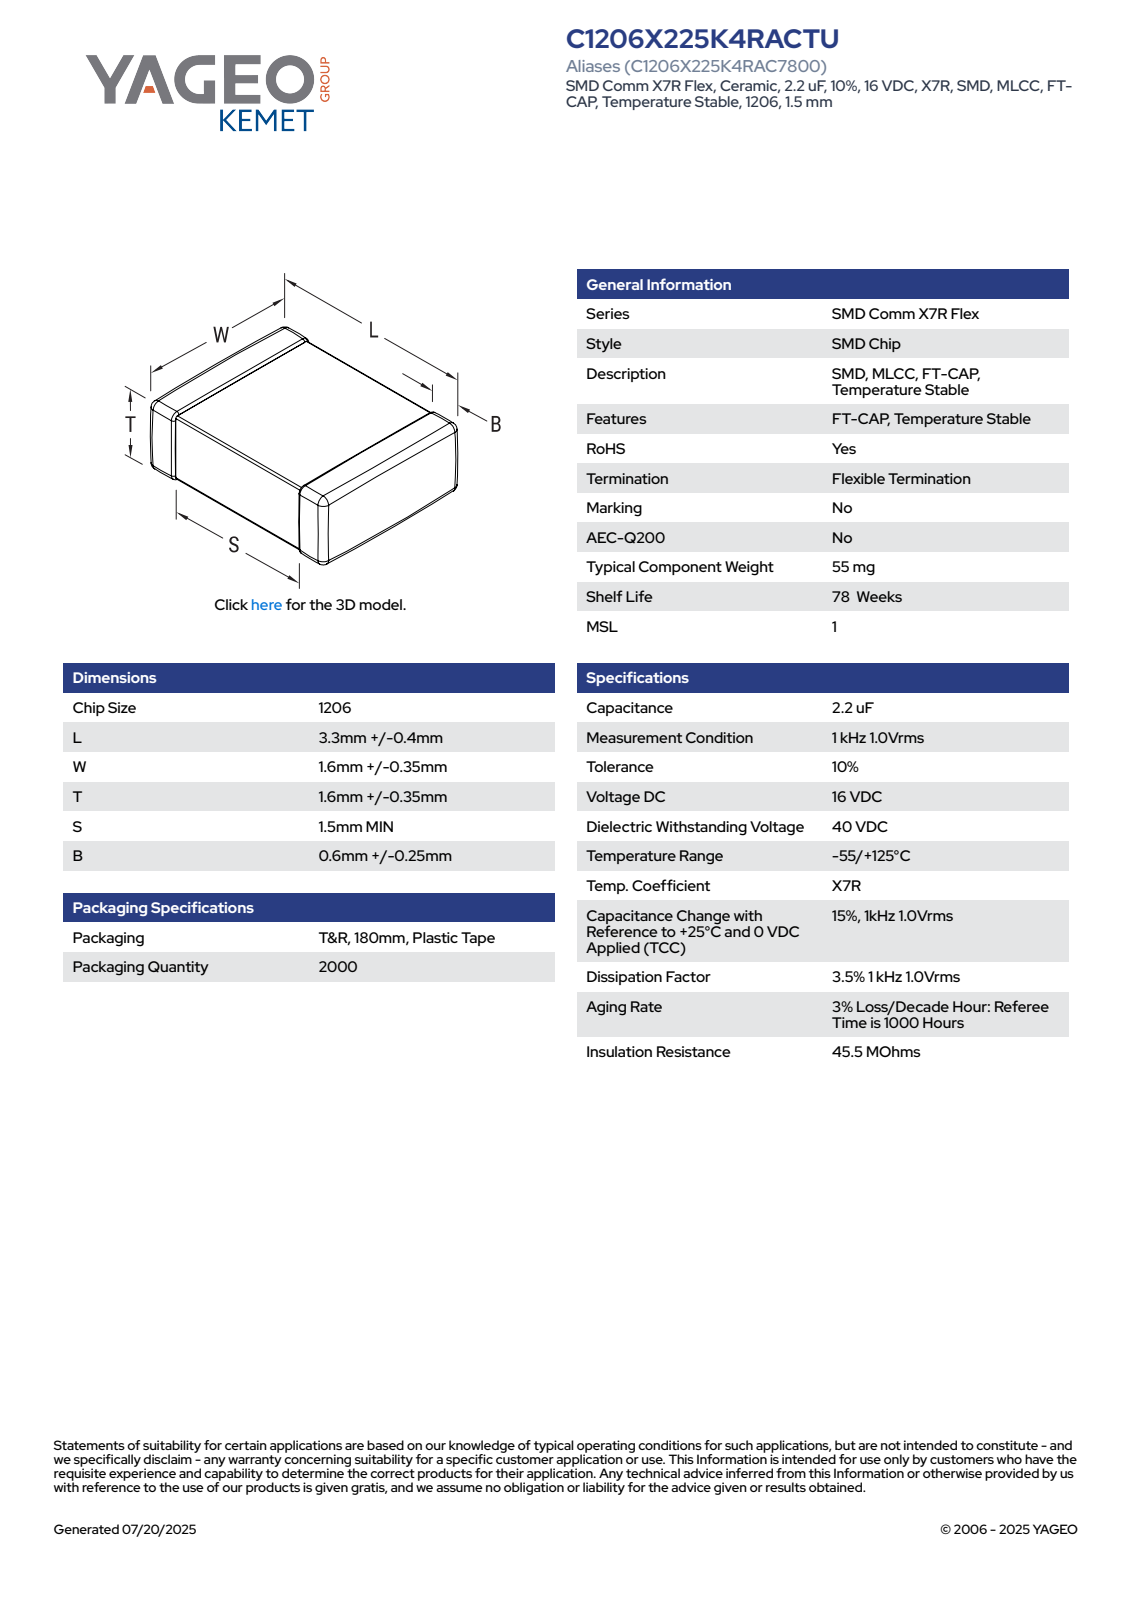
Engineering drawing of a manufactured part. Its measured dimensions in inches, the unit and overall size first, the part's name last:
Units: inches
Overall size (bounding box): 0.146 × 0.077 × 0.077
Main face-to-face distances: 0.075, 0.074, 0.077, 0.146, 0.034, 0.032, 0.041, 0.043, 0.039, 0.044
Volume: 0.001 in³ · Surface area: 0.056 in²
Bodies: 4 solids, 121 faces (71 planar, 34 cylindrical, 16 other)
Part name (STEP PRODUCT): CCS_CCSTDNOS_1206_L3.7W1.95T1.95B0.85
STEP written by: SolidWorks 2014 (AUTOMOTIVE_DESIGN)
